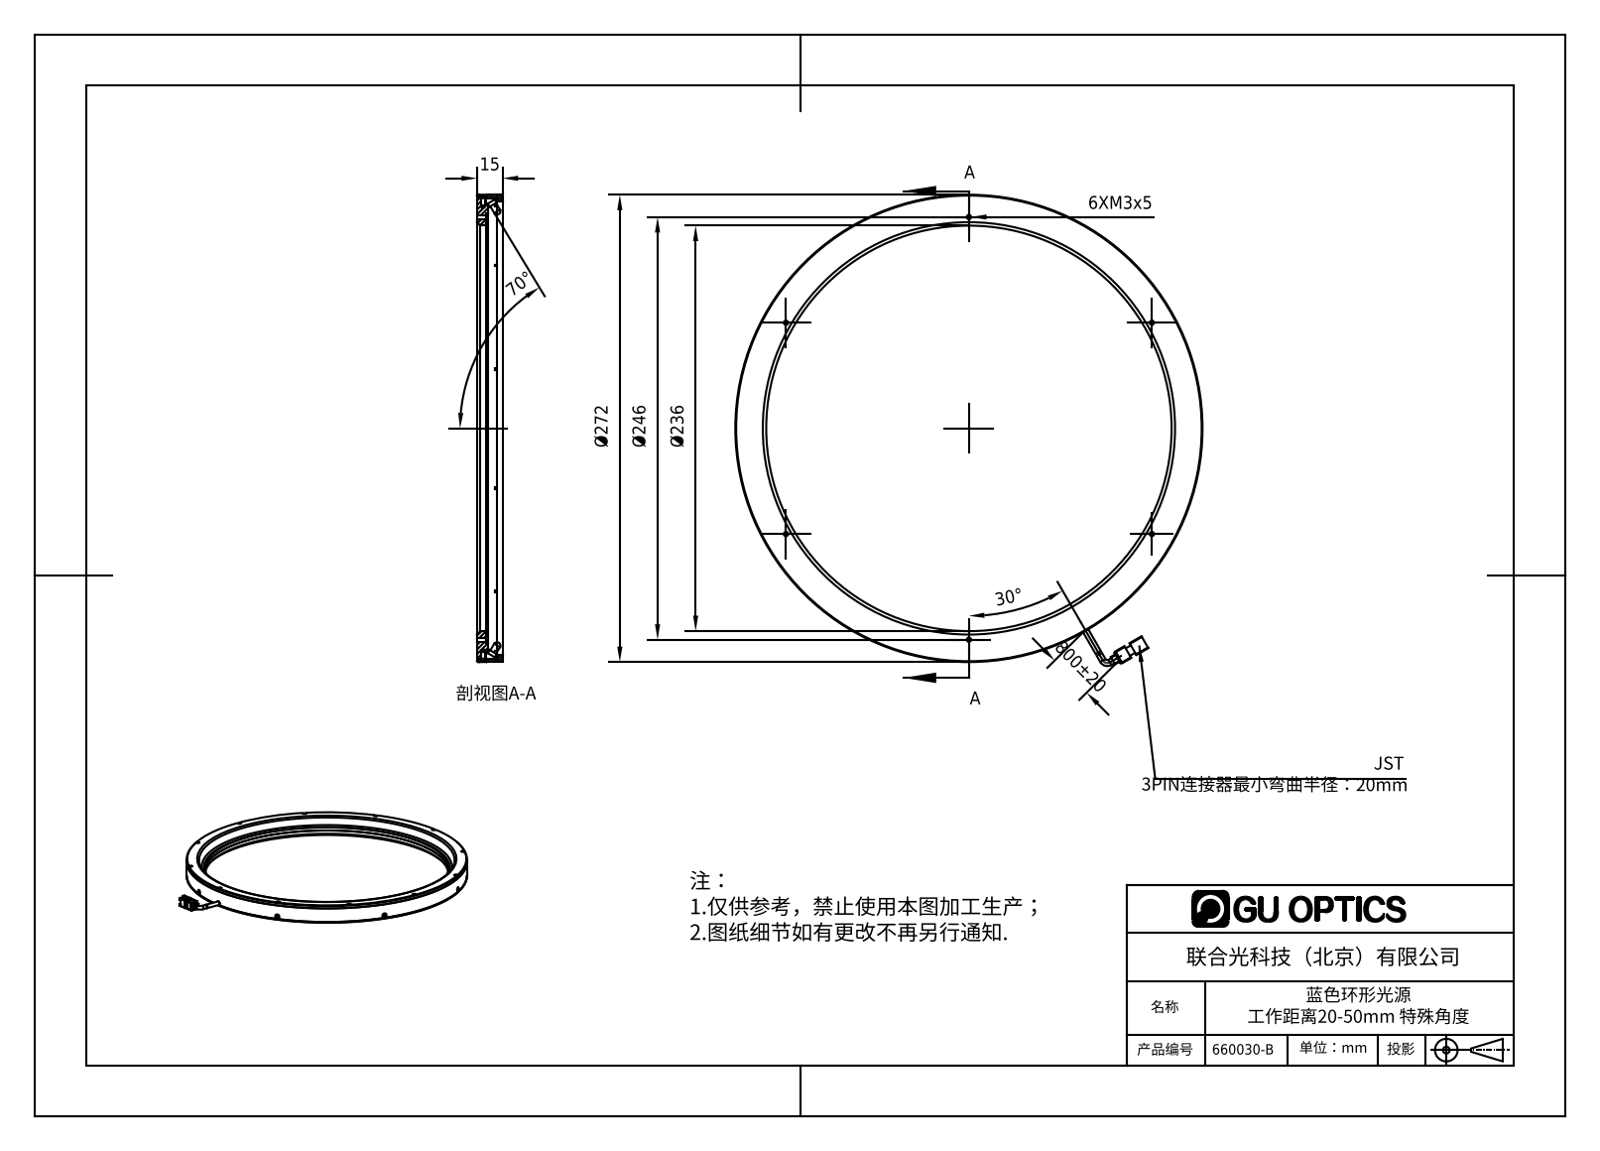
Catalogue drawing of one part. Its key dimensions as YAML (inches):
part_name: "660030-B"
step_written_by: "SolidWorks 2016 (AUTOMOTIVE_DESIGN)"
units: inches
bodies: {solids: 156, faces: 2958, planar: 1895, cylindrical: 793, other: 270}
overall_size: [10.801, 10.709, 0.757]
volume: 10.26
surface_area: 217.7
round_holes:
  - {diameter: 0.063, count: 18}
  - {diameter: 0.049, count: 12}
  - {diameter: 0.067, count: 12}
  - {diameter: 0.079, count: 6}
  - {diameter: 0.094, count: 6}
  - {diameter: 0.098, count: 6}
  - {diameter: 0.138, count: 1}
  - {diameter: 9.291, count: 1}
  - {diameter: 9.843, count: 1}
  - {diameter: 10.394, count: 1}
round_bosses_or_shafts:
  - {diameter: 0.15, count: 150}
  - {diameter: 0.118, count: 150}
  - {diameter: 0.138, count: 2}
  - {diameter: 10.709, count: 1}
  - {diameter: 10.551, count: 1}
  - {diameter: 10.236, count: 1}
partial_cylinders:
  - {radius: 0.02, count: 8}
  - {radius: 0.039, count: 4}
  - {radius: 0.063, count: 1}
  - {radius: 0.118, count: 1}
face_to_face_distances: [0.588, 0.118, 0.706, 0.209, 0.38, 0.498, 0.256, 0.332, 0.039, 0.047]
hole_center_spacings: [5.276, 1.377, 6.423, 9.748, 10.461, 2.731, 4.038, 10.192]
